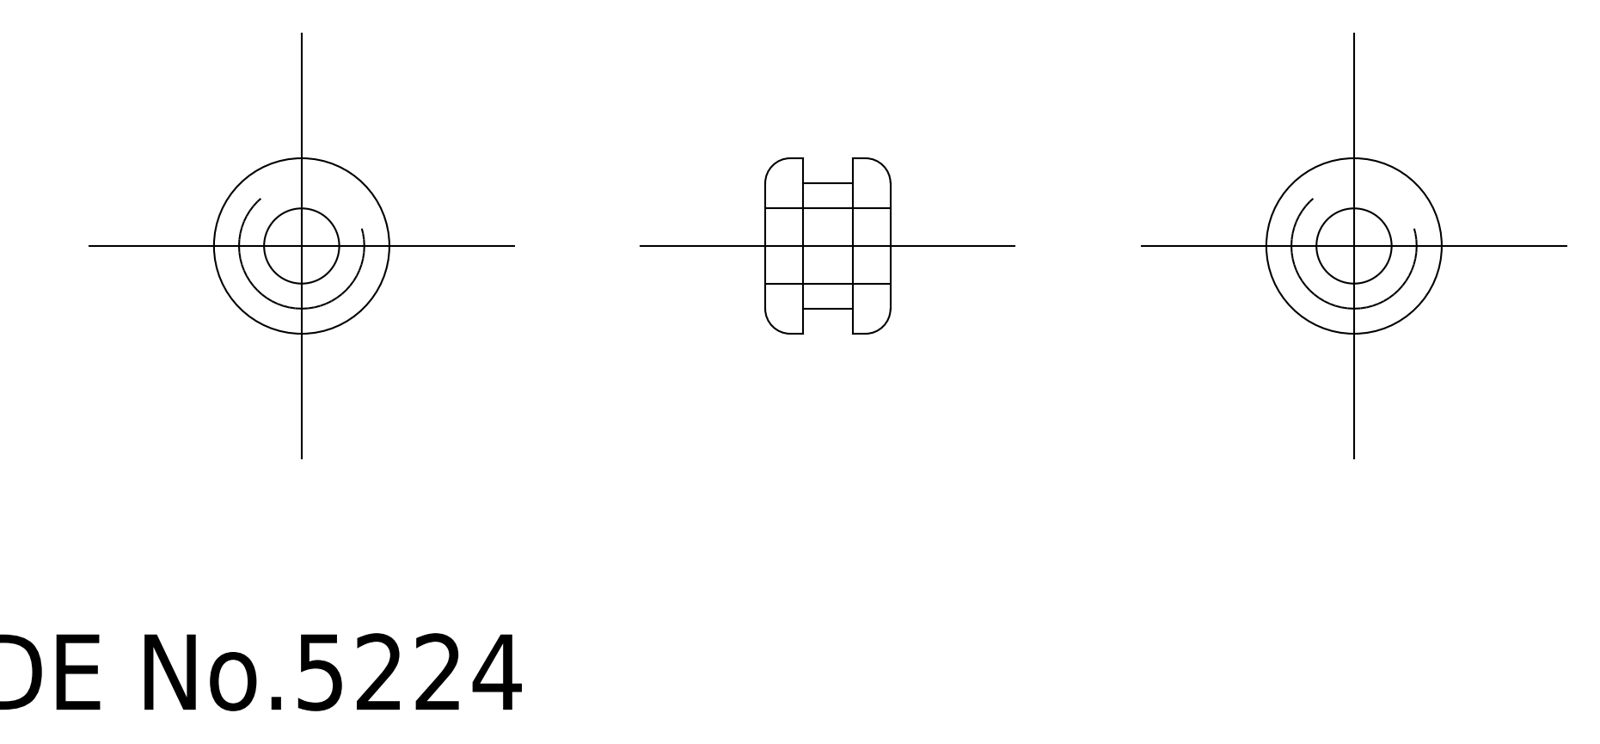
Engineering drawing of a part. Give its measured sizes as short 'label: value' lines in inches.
name: grommet
written by: CADfix (AUTOMOTIVE_DESIGN)
unit: in
bodies: 1 solid, 16 faces (0 planar, 0 cylindrical, 16 other)
size: 0.276 × 0.276 × 0.197
volume: 0.007 in³; area: 0.349 in²
